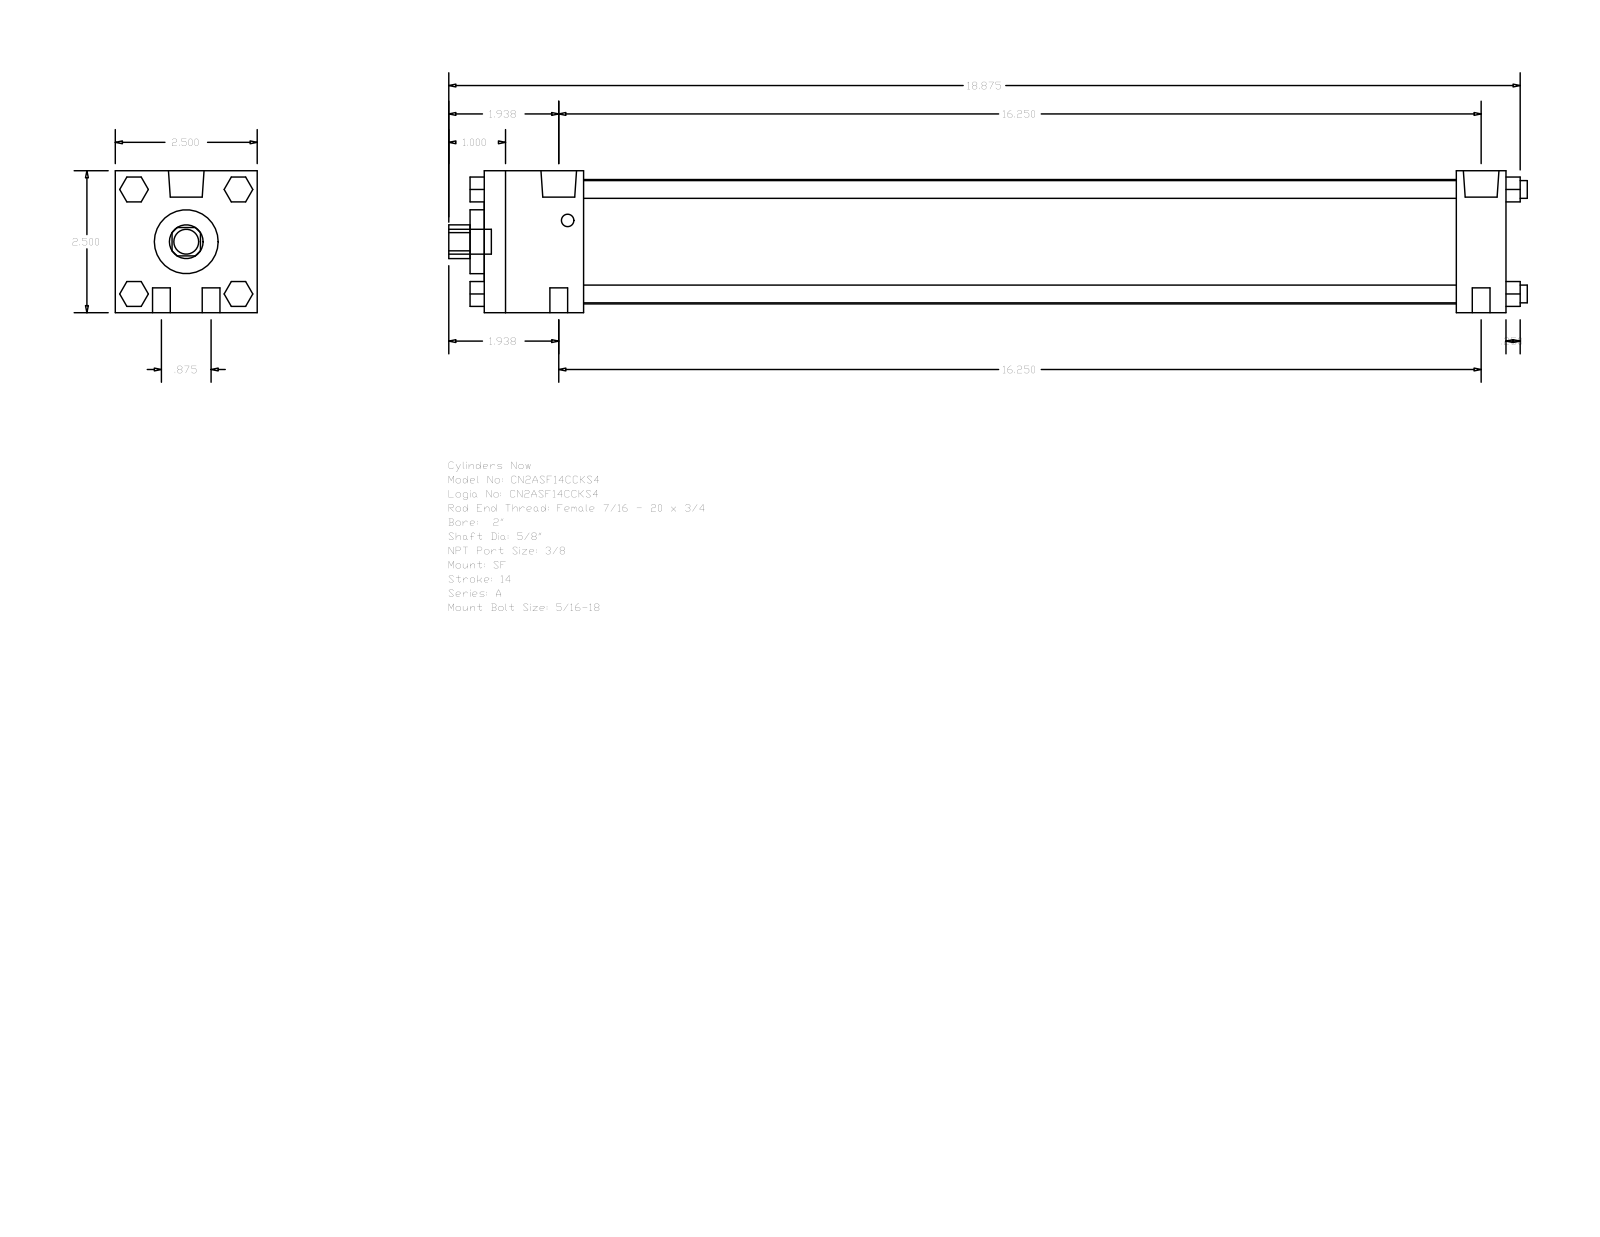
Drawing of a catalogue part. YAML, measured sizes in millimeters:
part_name: "A_SF__0200_0.625"
step_written_by: "GSSL Pune (CONFIG_CONTROL_DESIGN)"
units: millimeters
bodies: {solids: 0, faces: 124, planar: 94, cylindrical: 30, other: 0}
overall_size: [482.6, 63.5, 63.5]
round_holes:
  - {diameter: 15.88, count: 1}
  - {diameter: 28.57, count: 1}
  - {diameter: 55.63, count: 1}
round_bosses_or_shafts:
  - {diameter: 7.94, count: 8}
  - {diameter: 15.93, count: 2}
  - {diameter: 5.56, count: 2}
  - {diameter: 11.11, count: 1}
partial_cylinders:
  - {radius: 7.54, count: 1}
face_to_face_distances: [63.5, 457.19, 434.97, 22.22, 44.45, 390.52, 412.74, 50.8, 6.35, 441.32]
